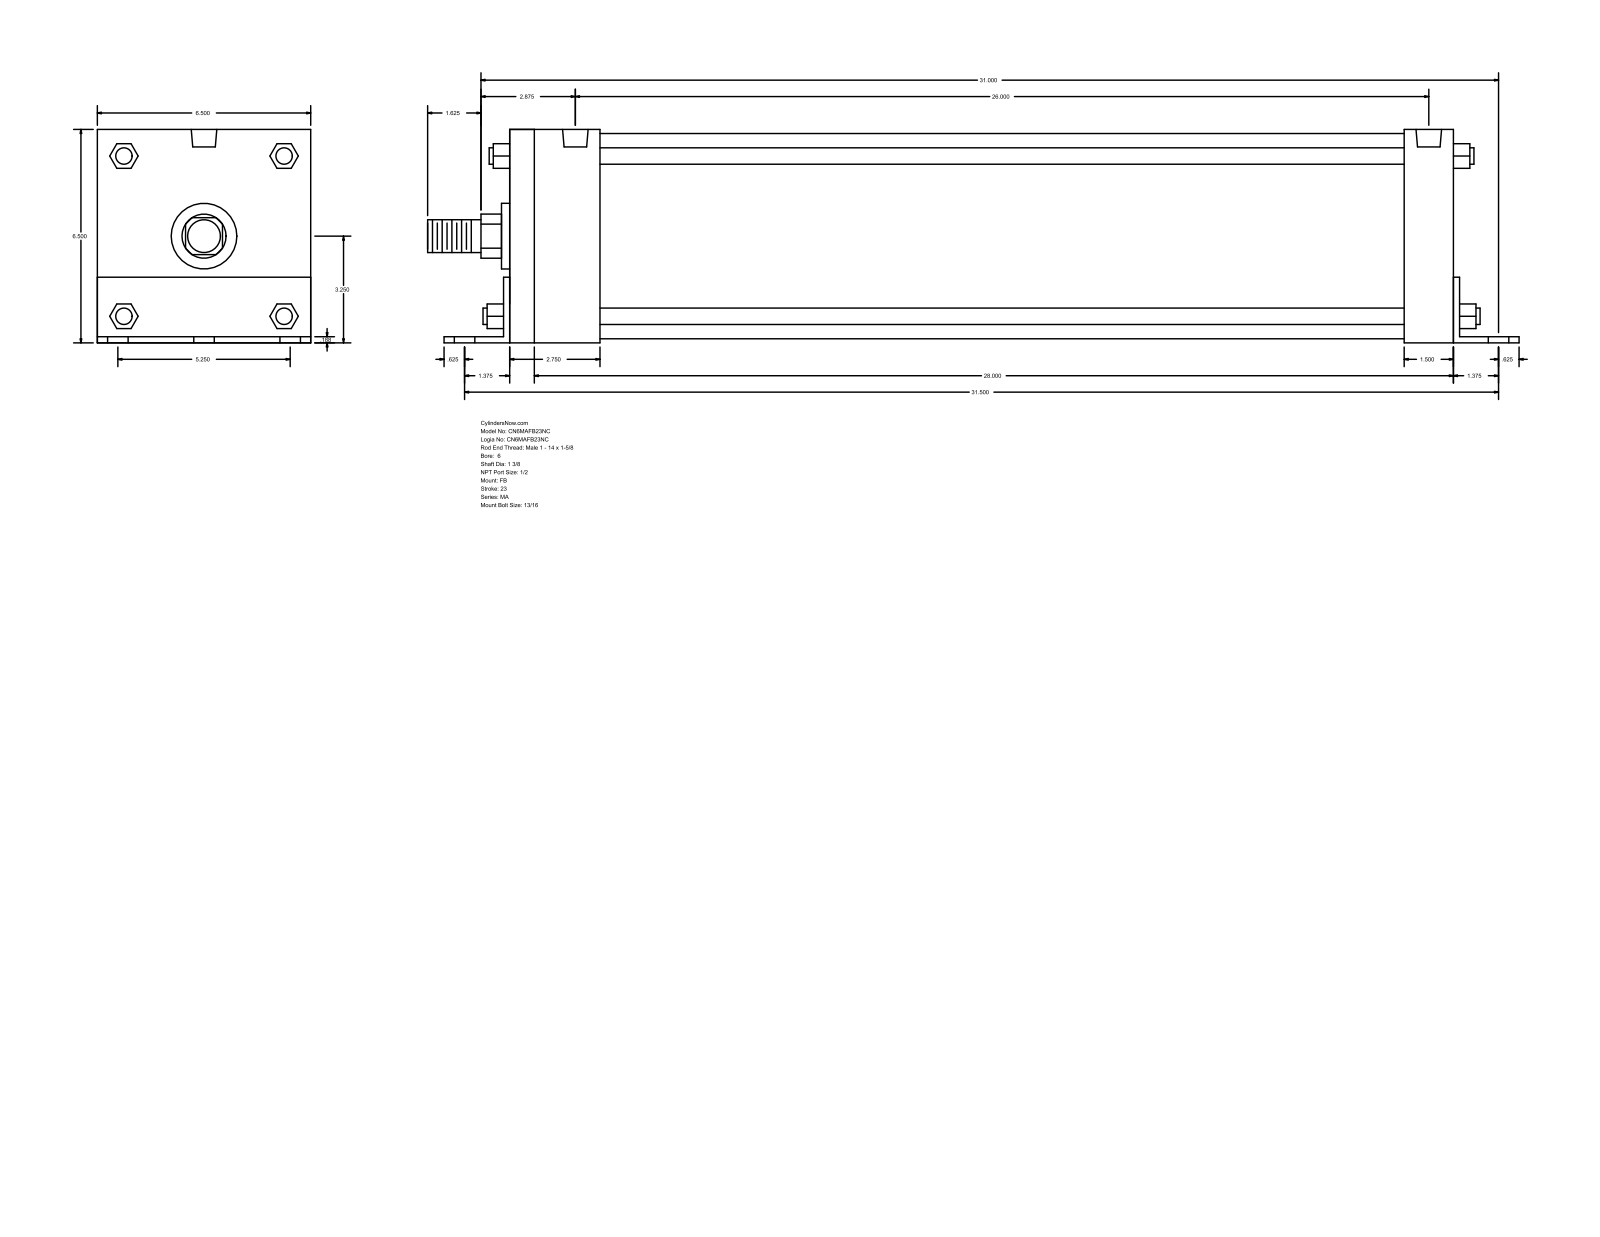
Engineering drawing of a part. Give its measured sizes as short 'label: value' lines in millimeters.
name: MA_FB__0600_1.375
written by: GSSL Pune (CONFIG_CONTROL_DESIGN)
unit: mm
bodies: 0 solids, 140 faces (105 planar, 35 cylindrical, 0 other)
size: 841.38 × 165.15 × 165.1
holes: 6× ⌀20.64, 4× ⌀17.46, 2× ⌀19.77
bosses: 4× ⌀12.7, 1× ⌀158.75, 1× ⌀50.8, 1× ⌀34.92, 1× ⌀25.4
rounds: 1× R17.06, 1× R32.05
face distances: 165.1, 4.76, 727.07, 165.15, 4.71, 160.39, 4.77, 38.1, 42.86, 736.6
hole spacings: 66.67, 799.71, 796.93, 83.82, 85.78, 108.6, 133.34, 657.22
